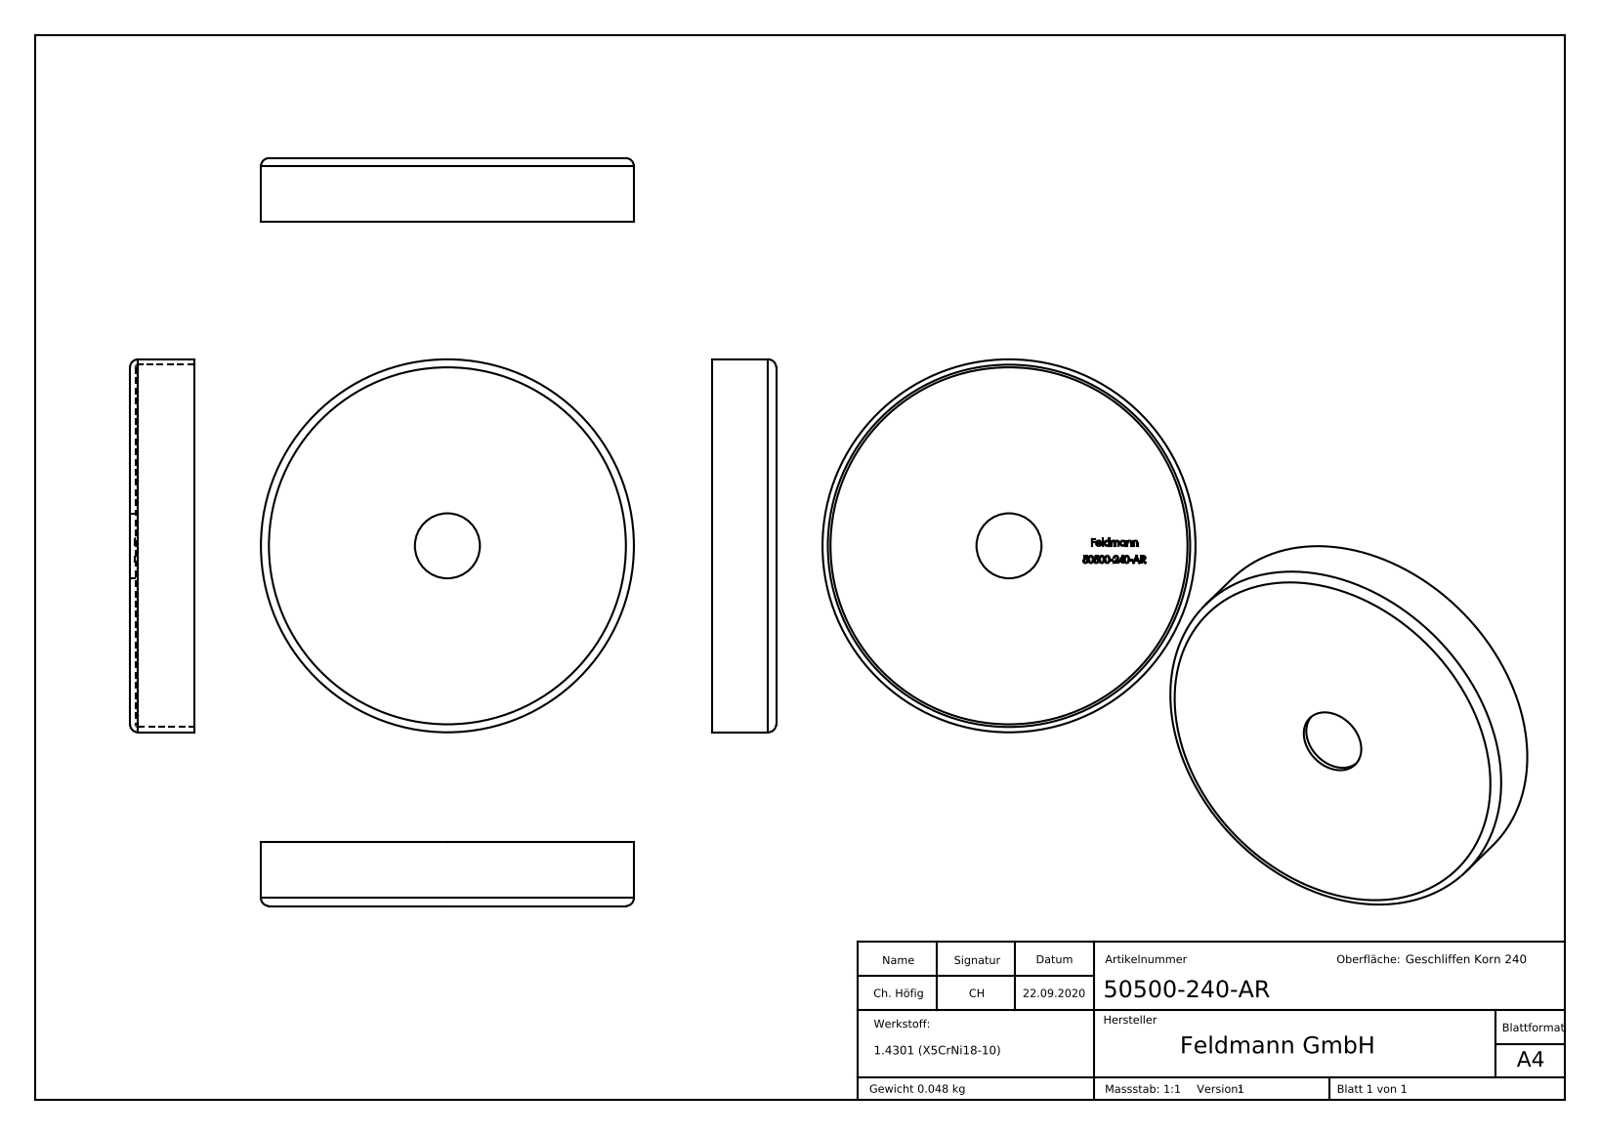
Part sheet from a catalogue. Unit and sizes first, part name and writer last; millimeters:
Units: millimetres
Overall size (bounding box): 70 × 70 × 12
Round holes (diameter × count): ⌀12.2 ×1, ⌀68 ×1
Round bosses / shafts (diameter × count): ⌀70 ×1
Main face-to-face distances: 1, 11, 12, 0.9, 11.1, 1.32, 0.39, 2.97, 0.88, 3.36
Volume: 6 022 mm³ · Surface area: 12 313 mm²
Bodies: 1 solid, 269 faces (148 planar, 6 cylindrical, 115 other)
Part name (STEP PRODUCT): 50500-240-AR
STEP written by: SolidWorks 2018 (CONFIG_CONTROL_DESIGN)
